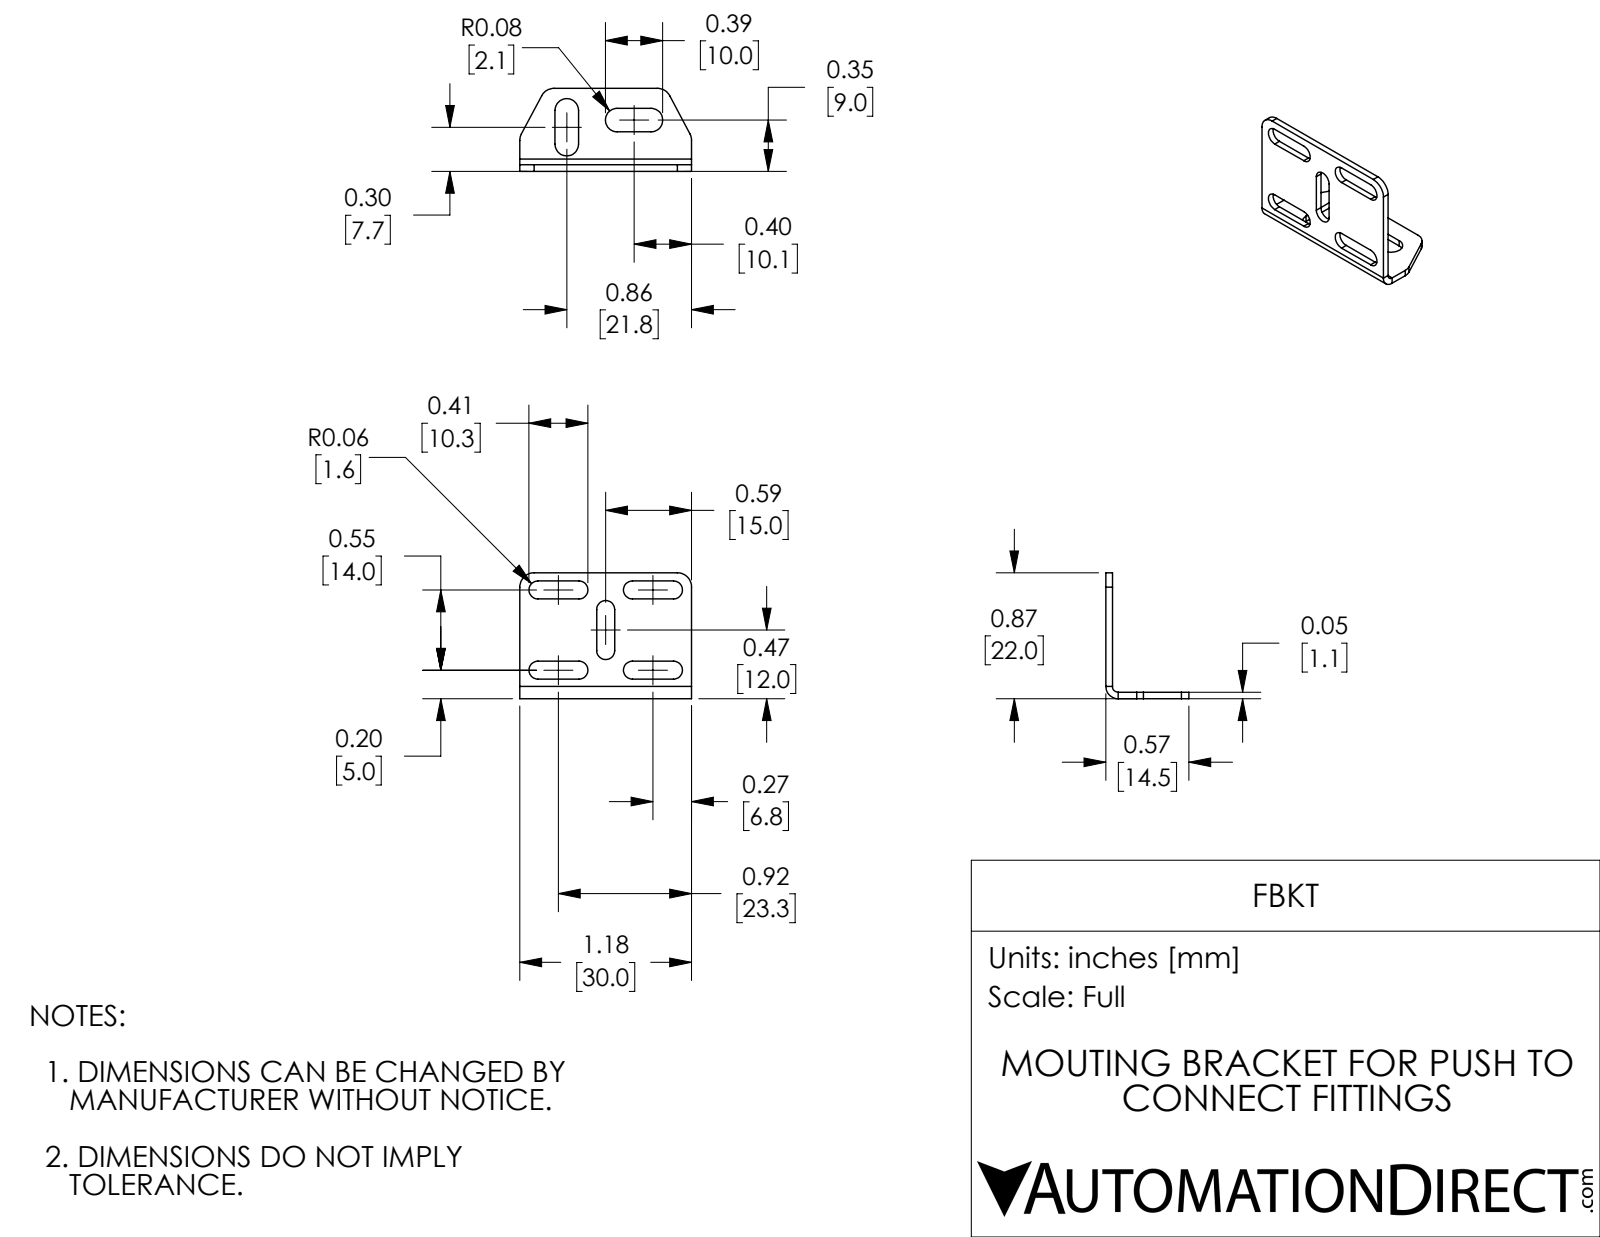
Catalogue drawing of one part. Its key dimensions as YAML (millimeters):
part_name: "FBKT"
step_written_by: "SolidWorks 2017 (AUTOMOTIVE_DESIGN)"
units: millimeters
bodies: {solids: 1, faces: 55, planar: 28, cylindrical: 27, other: 0}
overall_size: [30, 22, 14.5]
volume: 891
surface_area: 1885
partial_cylinders:
  - {radius: 1.57, count: 10}
  - {radius: 2.5, count: 6}
  - {radius: 2.05, count: 4}
  - {radius: 1.02, count: 1}
  - {radius: 2.16, count: 1}
face_to_face_distances: [1.14, 3.14, 14, 22, 20.86, 30, 13.36, 14.5, 6.57, 20.57]
